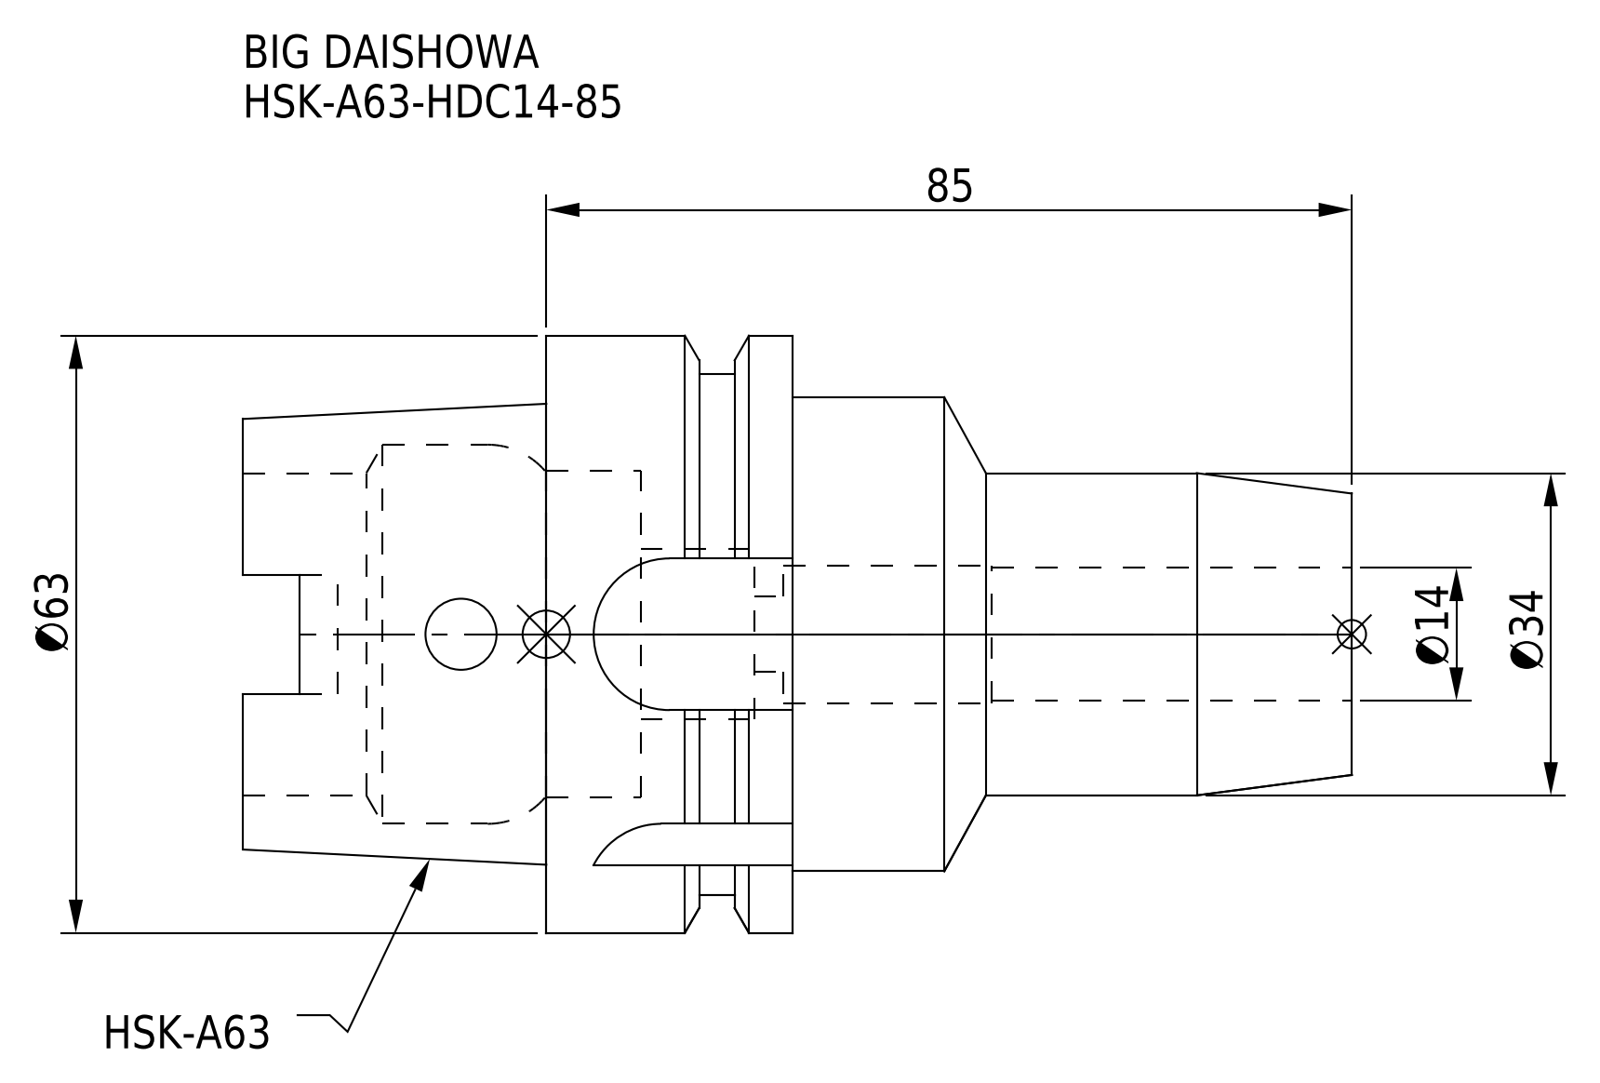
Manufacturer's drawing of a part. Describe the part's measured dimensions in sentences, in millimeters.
The part is named "HSK-A63-HDC14-85". Its 3-D file was written by "CREO PARAMETRIC BY PTC INC, 2016380 (AUTOMOTIVE_DESIGN)". It is 1 solid with 95 faces: 38 planar, 39 cylindrical and 18 other. Overall it measures 117 by 63 by 63 millimeters. Its volume is 143 009 cubic millimeters and its surface area 31 462 square millimeters. Round holes: 1 of diameter 7.5, 1 of diameter 8, 1 of diameter 14, 1 of diameter 14.5, 1 of diameter 18, 1 of diameter 34, 1 of diameter 34.5, 1 of diameter 40. Round bosses or shafts: 1 of diameter 63, 1 of diameter 55, 1 of diameter 50. Partial cylindrical surfaces (rounded edges, fillets, slot ends): 4 of radius 2.88, 4 of radius 8. The main face-to-face distances are 26, 16.05, 9.95, 59, 75.05, 85, 117, 58, 41.95, 32.
